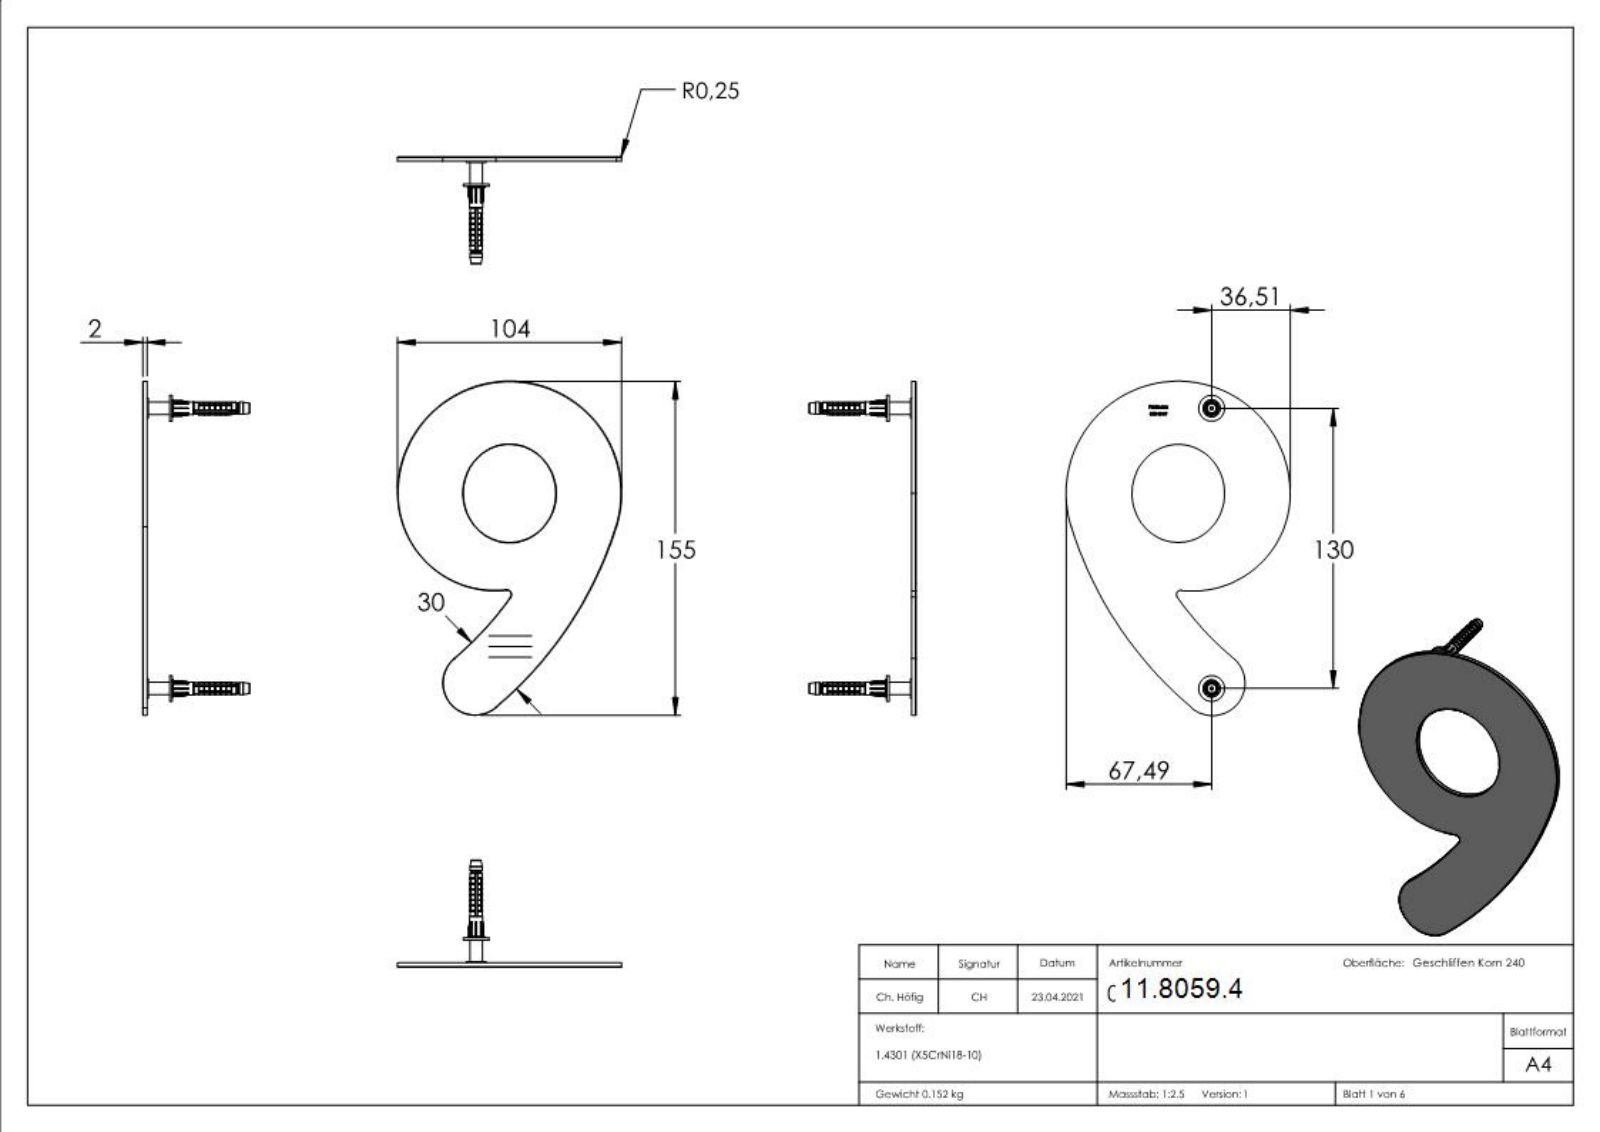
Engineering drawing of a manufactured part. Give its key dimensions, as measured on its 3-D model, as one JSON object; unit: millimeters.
{"part_name": "040-HN-X Teil2; 040-HN-X Teil3; 040-HN-X Teil1_040-HN-9 Teil1; 040-HN-9 (+5 more)", "step_written_by": "SolidWorks 2018 (CONFIG_CONTROL_DESIGN)", "units": "millimeters", "bodies": {"solids": 7, "faces": 1552, "planar": 355, "cylindrical": 385, "other": 812}, "overall_size": [10000, 5217.43, 4607.88], "volume_mm3": 20218, "surface_area_mm2": 23065, "round_holes": [[3.3, 2], [4.3, 2]], "round_bosses_or_shafts": [[12, 2], [9, 2], [8, 2], [6, 2], [5.8, 2], [5.6, 2], [4.6, 2], [4, 2]], "partial_cylinders_radius": [[0.1, 22], [3.5, 2], [2, 1], [15, 1], [45.31, 1], [52, 1], [150, 1], [180, 1]], "face_to_face_distances": [2, 11.6, 13.6, 1.1, 10.5, 12.5, 1, 0.5, 2.5, 10], "hole_center_spacings": [130]}
